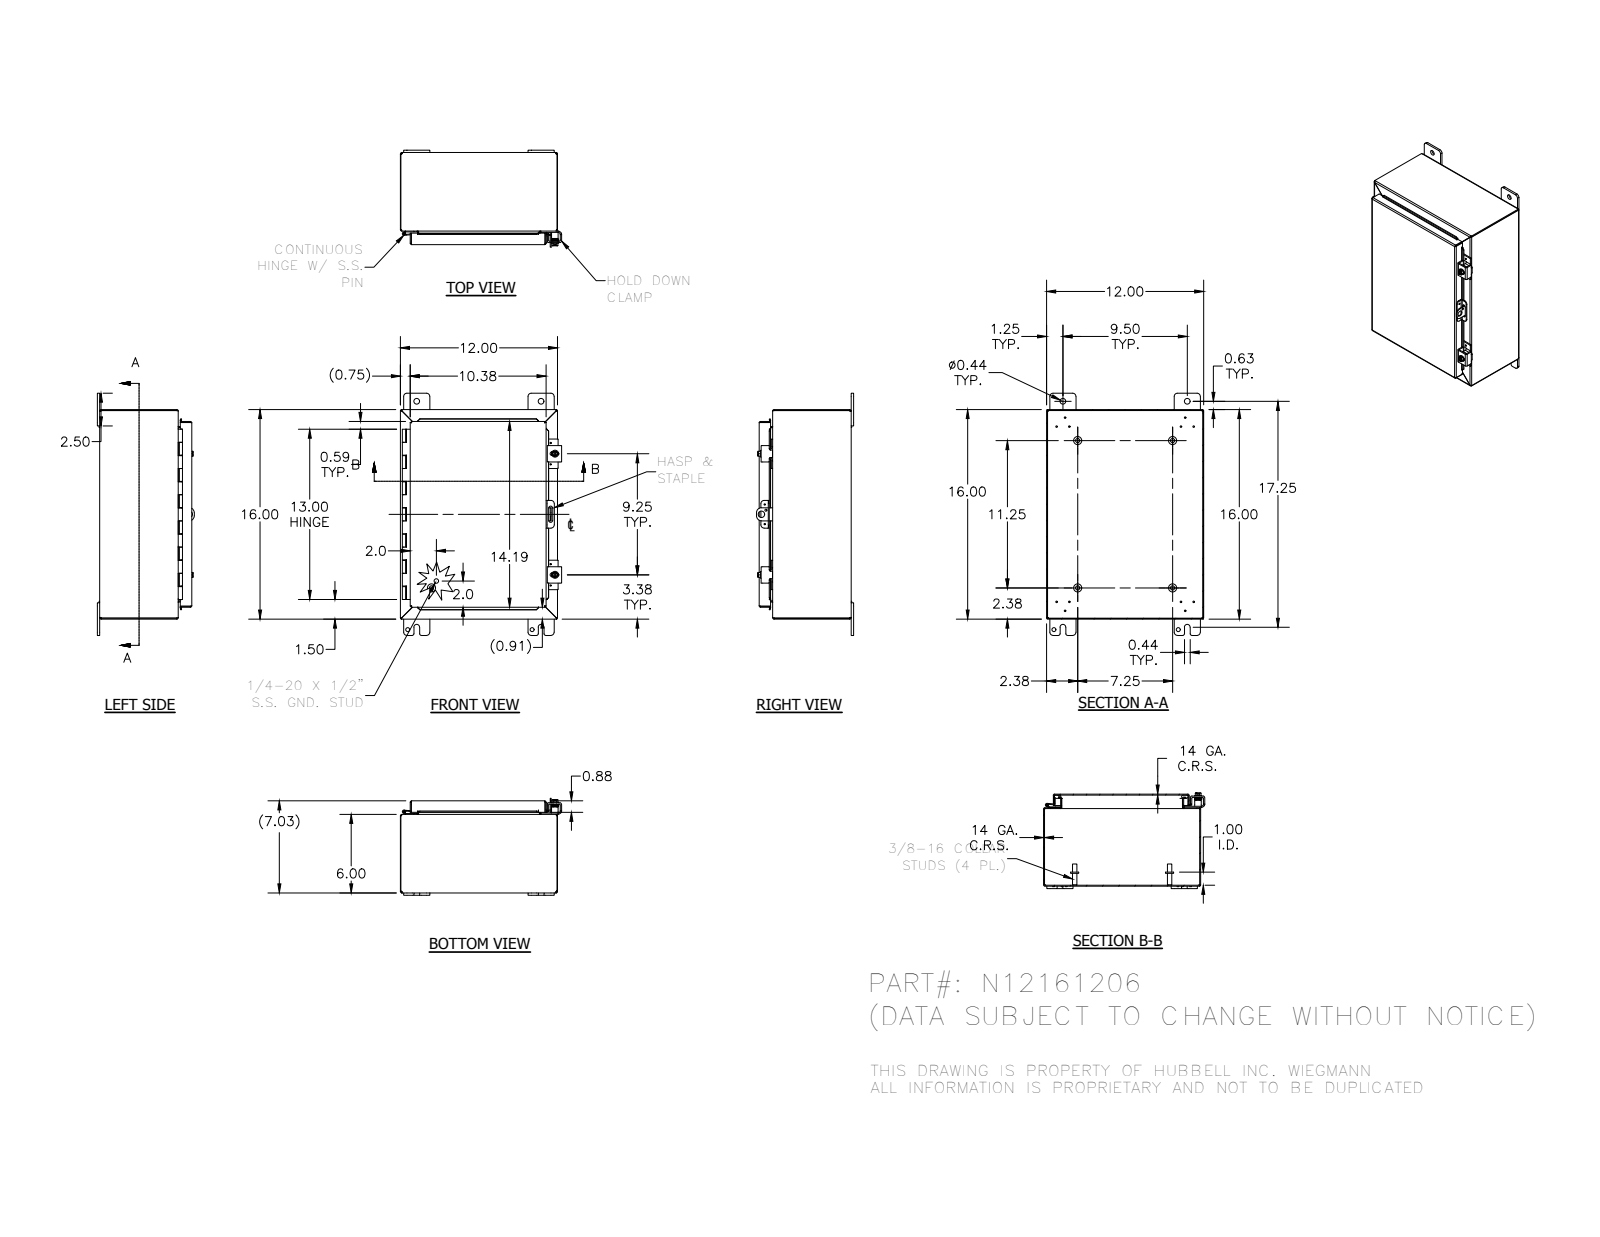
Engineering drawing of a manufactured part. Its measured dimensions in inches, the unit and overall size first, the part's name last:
Units: inches
Overall size (bounding box): 18.5 × 12.311 × 7.41
Round holes (diameter × count): ⌀0.12 ×12, ⌀0.11 ×7, ⌀0.313 ×4, ⌀0.438 ×4, ⌀0.211 ×2, ⌀0.281 ×2, ⌀0.3 ×2, ⌀0.125 ×1, ⌀0.156 ×1, ⌀0.5 ×1
Round bosses / shafts (diameter × count): ⌀0.625 ×4, ⌀0.33 ×4, ⌀0.25 ×4, ⌀0.52 ×2, ⌀0.5 ×2, ⌀0.35 ×2, ⌀0.115 ×2, ⌀0.337 ×1
Partial cylindrical surfaces — rounded edges, fillets, slot ends (radius × count): R0.03 ×27, R0.063 ×25, R0.125 ×25, R0.25 ×25, R0.031 ×23, R0.105 ×23, R0.07 ×8, R0.1 ×4
Main face-to-face distances: 0.074, 6.959, 11.926, 6.885, 7.033, 15.926, 5.926, 1.033, 11.852, 12
Hole centre spacings: 9.5, 0.759, 0.839, 0.94, 0.969, 1.593, 1.995, 8.883
Volume: 72.71 in³ · Surface area: 1 863 in²
Bodies: 27 solids, 914 faces (489 planar, 308 cylindrical, 117 other)
Part name (STEP PRODUCT): N12161206; 34840; 38420; N12161206BKP (+8 more)
STEP written by: Autodesk Inventor 2012 (AUTOMOTIVE_DESIGN)
